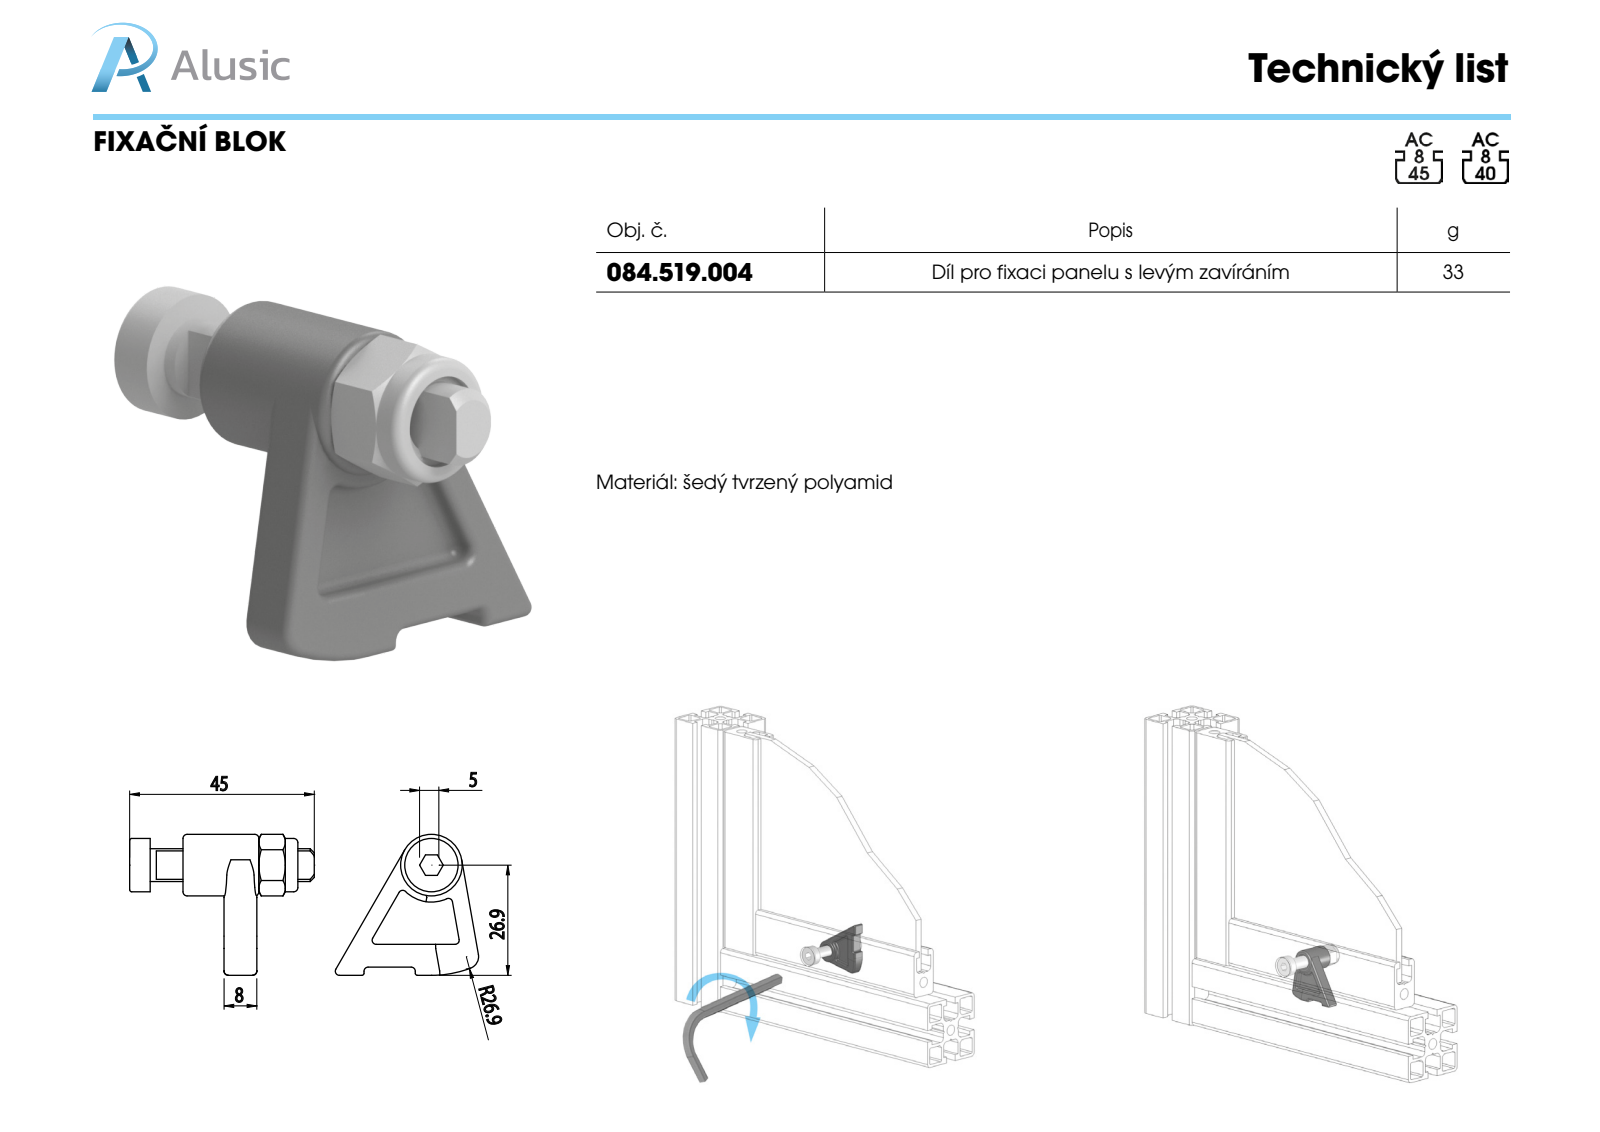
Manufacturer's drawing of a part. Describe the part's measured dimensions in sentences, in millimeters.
The part is named "084.519.004; 985-A2; 084.519.005; 084.519.004L". Its 3-D file was written by "SolidWorks 2011 (CONFIG_CONTROL_DESIGN)". It is 3 solids with 221 faces: 43 planar, 76 cylindrical and 102 other. Overall it measures 45 by 34.93 by 34.36 millimeters. Its volume is 9 001 cubic millimeters and its surface area 5 720 square millimeters. Round holes: 1 of diameter 6.8, 1 of diameter 8, 1 of diameter 9.43. Round bosses or shafts: 1 of diameter 15, 1 of diameter 13. Partial cylindrical surfaces (rounded edges, fillets, slot ends): 33 of radius 1, 2 of radius 0.5, 1 of radius 3, 1 of radius 4.1, 1 of radius 9, 1 of radius 26.85. The main face-to-face distances are 2.5, 5.5, 3, 8, 13, 8.5, 6, 18, 0.5, 5.
